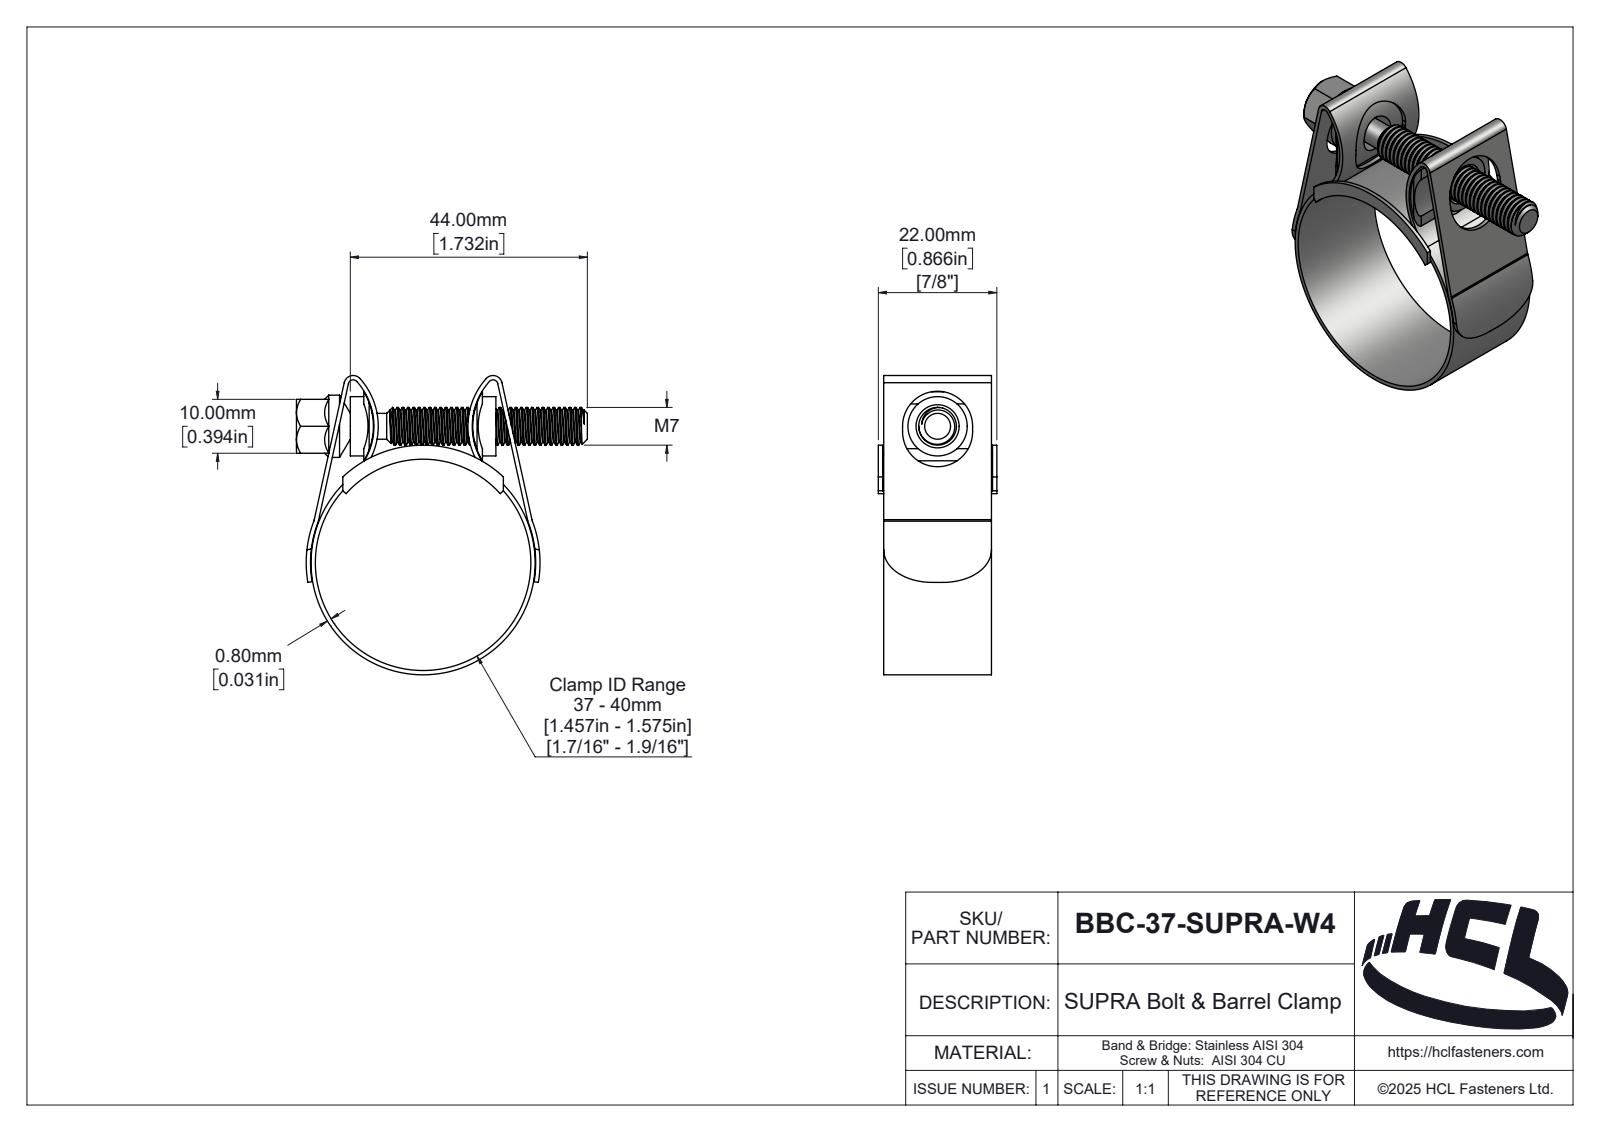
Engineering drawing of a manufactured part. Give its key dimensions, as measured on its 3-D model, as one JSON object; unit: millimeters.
{"part_name": "BBC-37-SUPRA-W4", "step_written_by": "SolidWorks 2025 (AUTOMOTIVE_DESIGN)", "units": "millimeters", "bodies": {"solids": 5, "faces": 309, "planar": 46, "cylindrical": 184, "other": 79}, "overall_size": [55.52, 54, 22], "volume_mm3": 6569, "surface_area_mm2": 12947, "round_holes": [[40, 1]], "round_bosses_or_shafts": [[11.55, 1], [11, 1], [7, 1], [4.8, 1]], "partial_cylinders_radius": [[1, 4], [0.9, 2], [1.7, 2], [2, 2], [2.8, 2], [6.5, 2], [11.36, 2], [12.36, 2]], "face_to_face_distances": [0.8, 1, 21, 20, 10, 21.2, 20.2, 2.5, 24.52, 22]}
